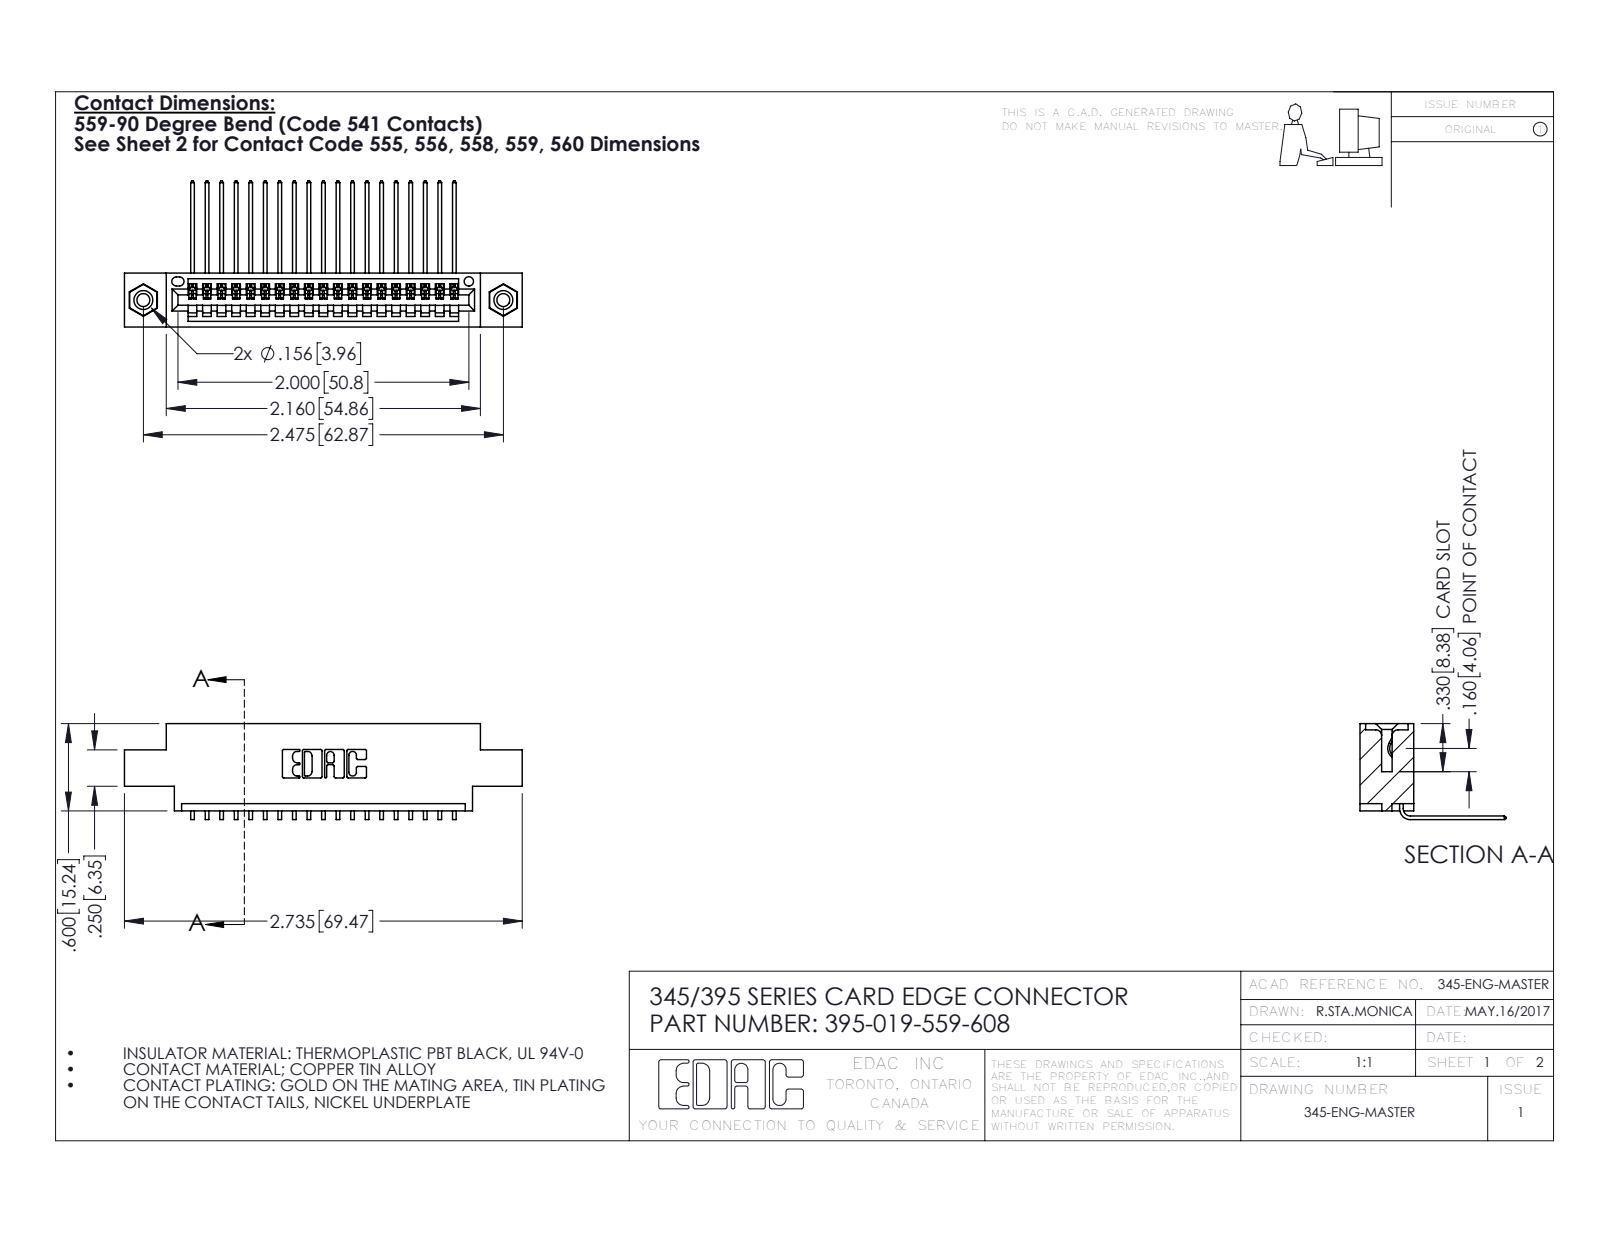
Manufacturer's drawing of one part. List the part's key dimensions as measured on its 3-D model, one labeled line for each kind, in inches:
Part name (STEP PRODUCT): 395-019-559-608; 345-250-001_345-250-003-102; 345-292-001_558 559 Tail - 1; 345 Part_0.170 Offset - 0.156 Dia-TI
STEP written by: SolidWorks 2016 (CONFIG_CONTROL_DESIGN)
Units: inches
Bodies: 22 solids, 1330 faces (914 planar, 400 cylindrical, 16 other)
Overall size (bounding box): 2.735 × 1.005 × 0.659
Volume: 0.388 in³ · Surface area: 13.4 in²
Round holes (diameter × count): ⌀0.089 ×2, ⌀0.125 ×2, ⌀0.156 ×2, ⌀0.064 ×1
Round bosses / shafts (diameter × count): ⌀0.155 ×2
Partial cylindrical surfaces — rounded edges, fillets, slot ends (radius × count): R0.006 ×38, R0.01 ×22, R0.007 ×6, R0.031 ×6, R0.026 ×3, R0.031 ×2, R0.04 ×2, R0.014 ×1
Main face-to-face distances: 0.072, 0.298, 0.37, 0.2, 0.098, 0.272, 0.025, 0.225, 0.1, 0.15
Hole centre spacings: 0.27, 2.241, 2.475
